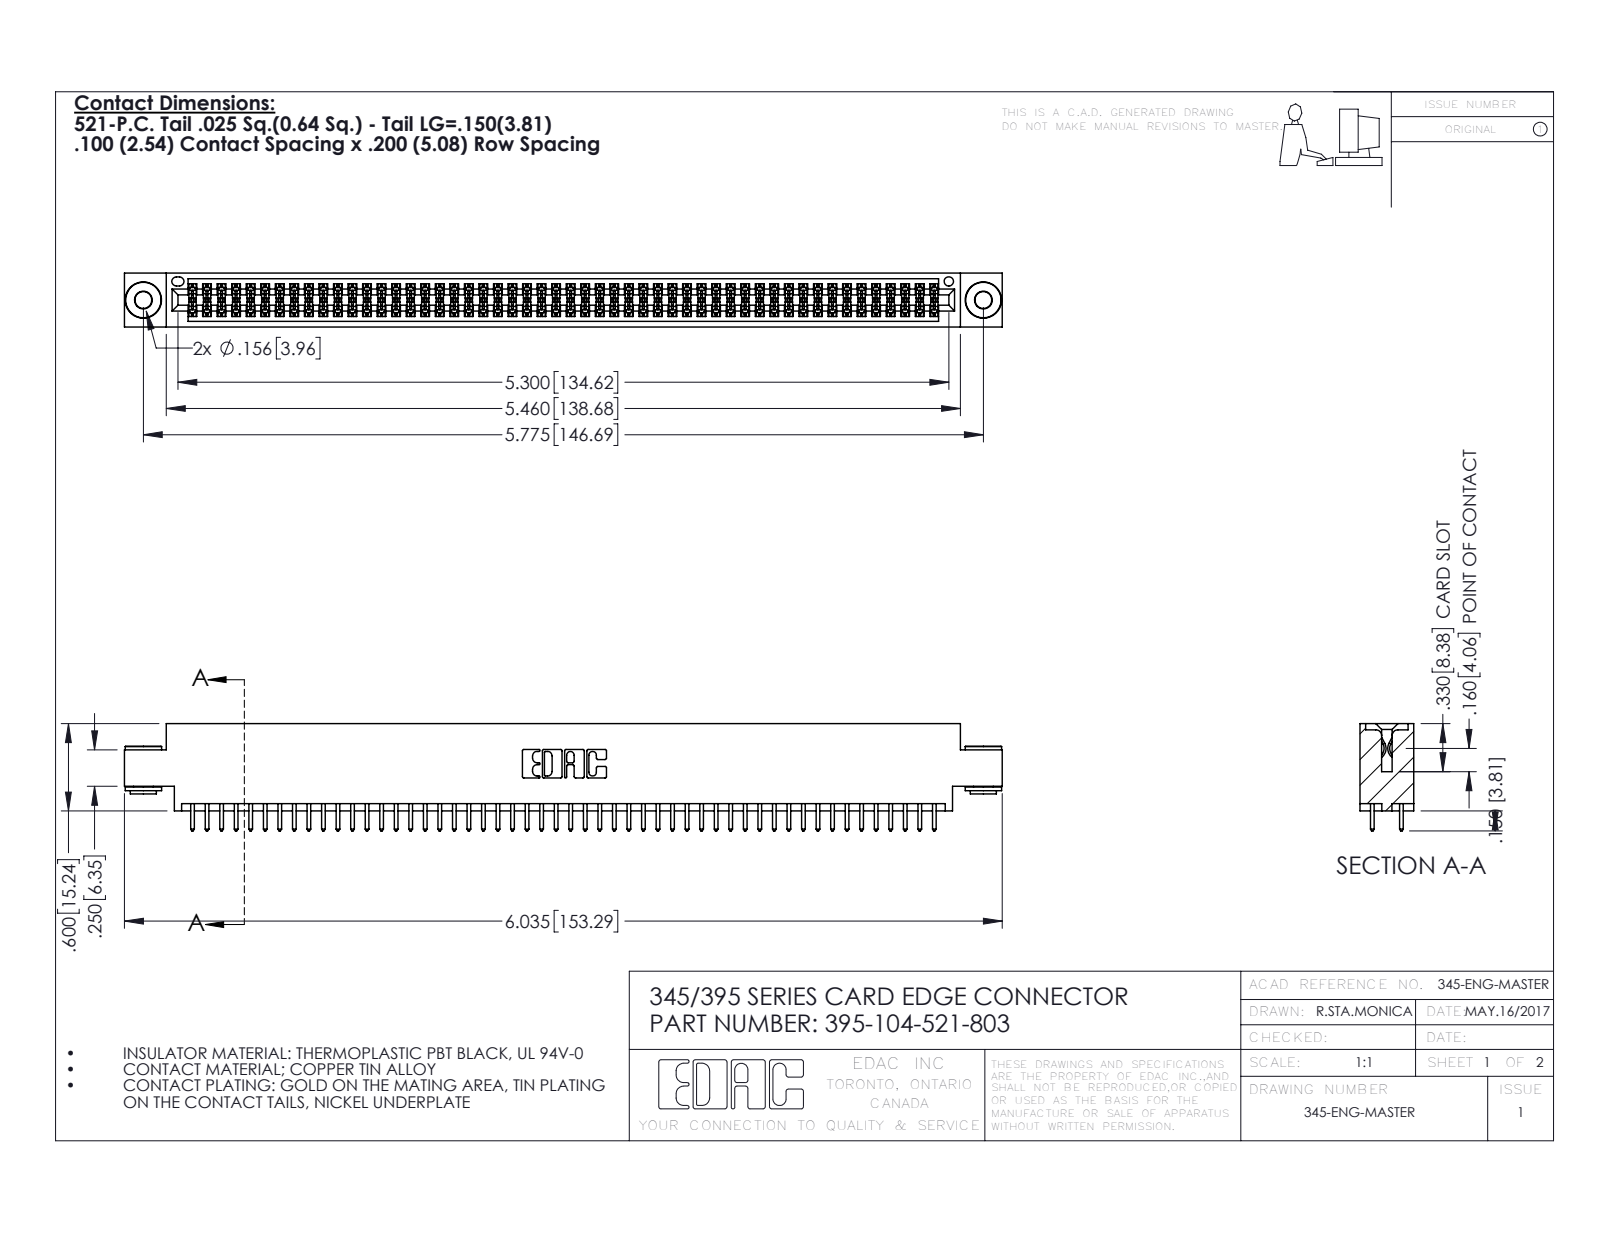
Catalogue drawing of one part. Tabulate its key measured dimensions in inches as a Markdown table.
| quantity | value |
| --- | --- |
| part name | 345-292-001_345-293-121; 345 Part_0.170 Offset - 0.156 Dia-TH; 395-104-521-803; 345-250-002_345-250-002-102 |
| STEP written by | SolidWorks 2016 (CONFIG_CONTROL_DESIGN) |
| units | inches |
| bodies | 107 solids, 5368 faces (3526 planar, 1834 cylindrical, 8 other) |
| overall size | 6.035 × 0.737 × 0.37 |
| volume | 0.906 in³ |
| surface area | 34.43 in² |
| round holes (diameter × count) | 0.116 × 2, 0.156 × 2, 0.064 × 1 |
| round bosses / shafts (diameter × count) | 0.25 × 2, 0.18 × 2, 0.136 × 2 |
| partial cylindrical surfaces (radius × count) | 0.006 × 156, 0.01 × 104, 0.01 × 22, 0.007 × 6, 0.031 × 6, 0.026 × 3, 0.014 × 2, 0.019 × 2 |
| main face-to-face distances | 0.072, 0.298, 0.37, 0.2, 0.098, 0.272, 0.025, 0.225, 0.175, 0.149 |
| hole center spacings | 0.27, 5.539, 5.775 |
